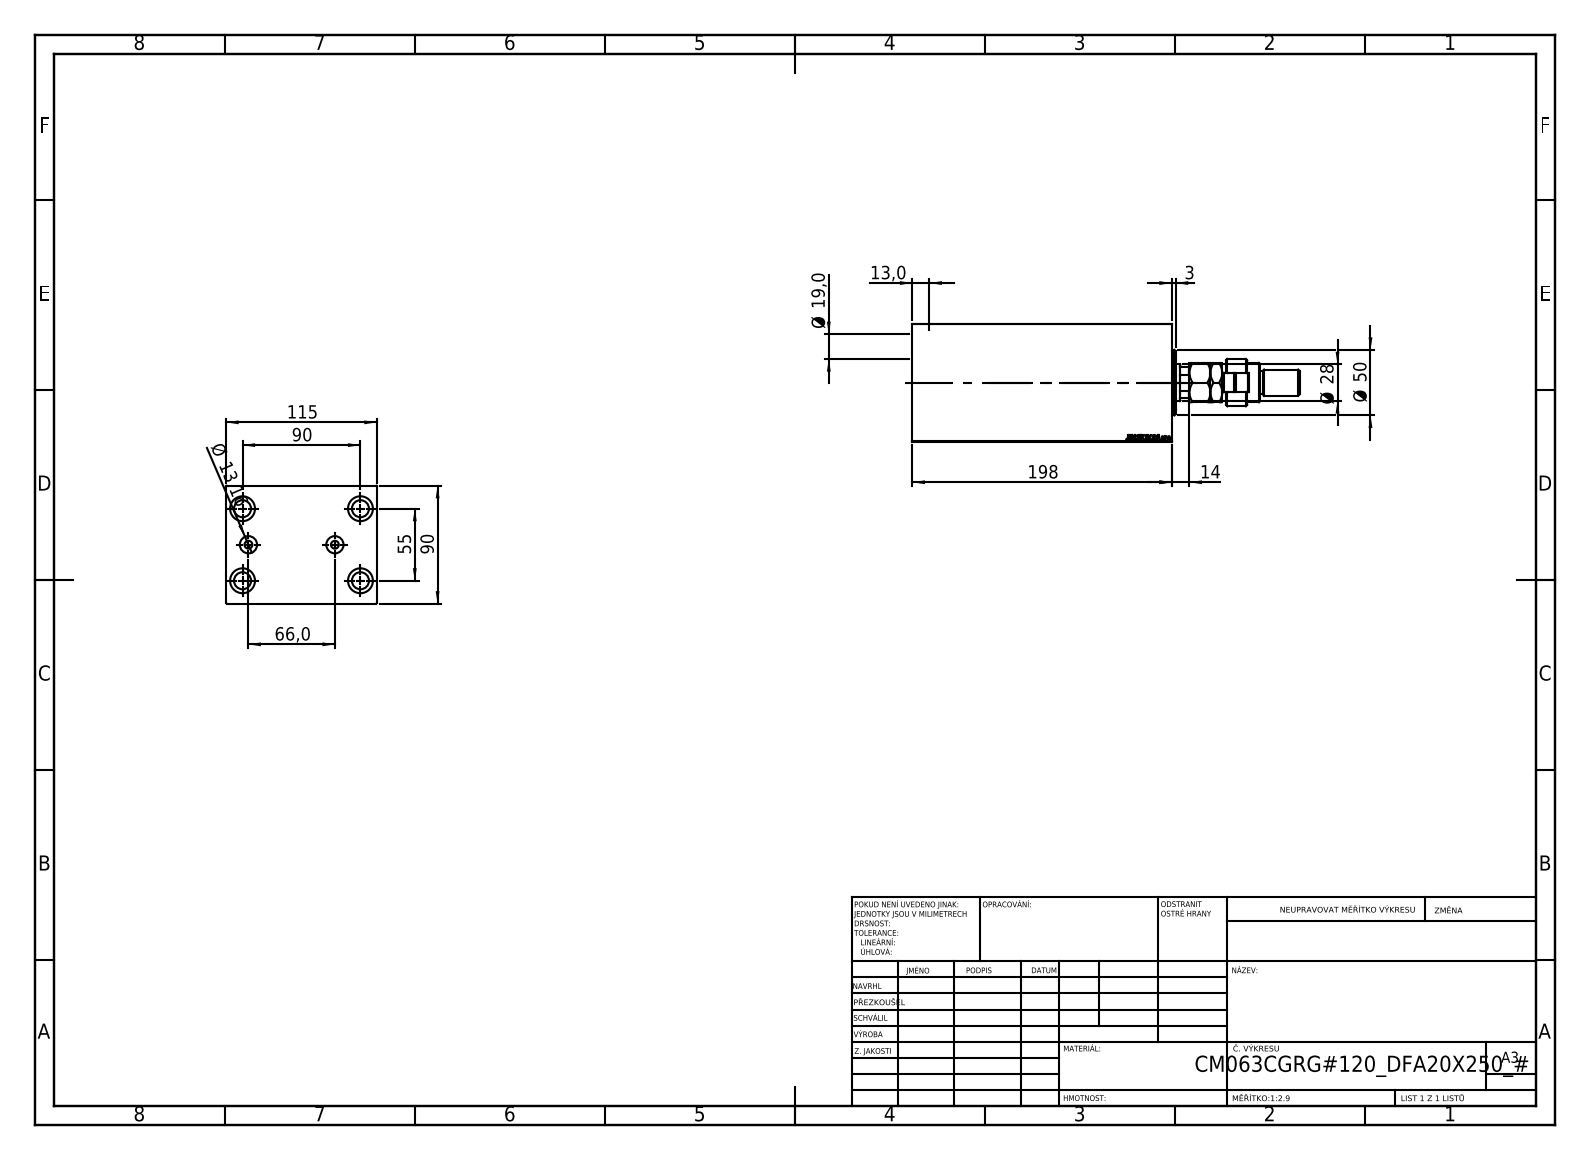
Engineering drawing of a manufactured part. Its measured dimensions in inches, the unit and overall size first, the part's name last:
Units: inches
Overall size (bounding box): 11.634 × 4.528 × 3.543
Round holes (diameter × count): ⌀0.512 ×4, ⌀0.748 ×4, ⌀0.236 ×2, ⌀0.518 ×2, ⌀0.728 ×1, ⌀1.102 ×1, ⌀1.24 ×1, ⌀2.48 ×1, ⌀2.559 ×1, ⌀2.835 ×1
Round bosses / shafts (diameter × count): ⌀1.969 ×1, ⌀1.417 ×1, ⌀1.181 ×1, ⌀0.866 ×1, ⌀0.787 ×1, ⌀0.709 ×1, ⌀0.551 ×1
Partial cylindrical surfaces — rounded edges, fillets, slot ends (radius × count): R0.295 ×1, R0.472 ×1, R0.531 ×1
Main face-to-face distances: 3.543, 4.528, 7.795, 0.689, 7.106, 0.531, 6.575, 7.264, 2.539, 1.85
Hole centre spacings: 2.076, 1.097, 1.327, 2.165, 2.979, 3.536, 3.543, 4.153
Volume: 102.1 in³ · Surface area: 356.4 in²
Bodies: 5 solids, 945 faces (436 planar, 71 cylindrical, 438 other)
Part name (STEP PRODUCT): V450CM_C_Body; V450CM_VC_B; MFA; V450CM_C_VCP (+1 more)
STEP written by: SolidWorks 2019 (CONFIG_CONTROL_DESIGN)
